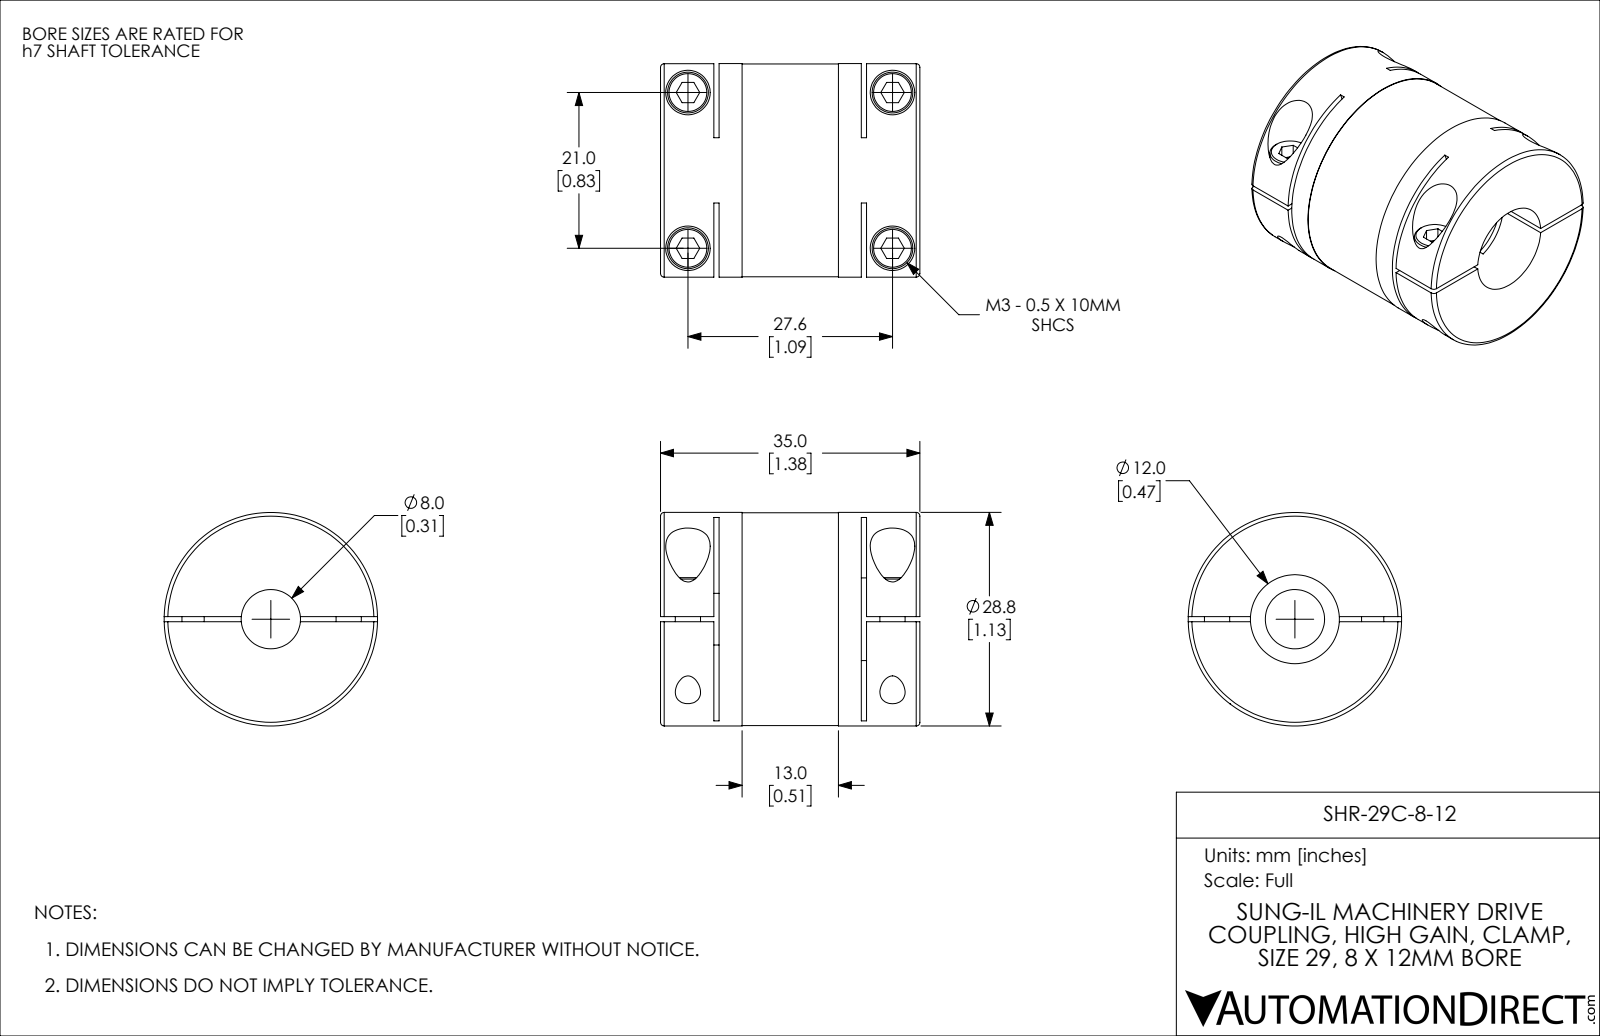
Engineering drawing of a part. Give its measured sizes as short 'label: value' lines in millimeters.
name: SHR-29C-8-12
written by: SolidWorks 2021 (CONFIG_CONTROL_DESIGN)
unit: mm
bodies: 1 solid, 145 faces (70 planar, 57 cylindrical, 18 other)
size: 35 × 28.8 × 28.8
volume: 17 462 mm³; area: 8 965 mm²
holes: 4× ⌀3.4, 4× ⌀6, 1× ⌀8, 1× ⌀12, 1× ⌀14
bosses: 4× ⌀5.5, 2× ⌀3, 1× ⌀28.8, 1× ⌀28.7
rounds: 2× R37.5
face distances: 0.7, 7.9, 27.1, 7.2, 27.8, 19.9, 35, 19.2, 20.6, 11
hole spacings: 21, 27.6, 34.68
